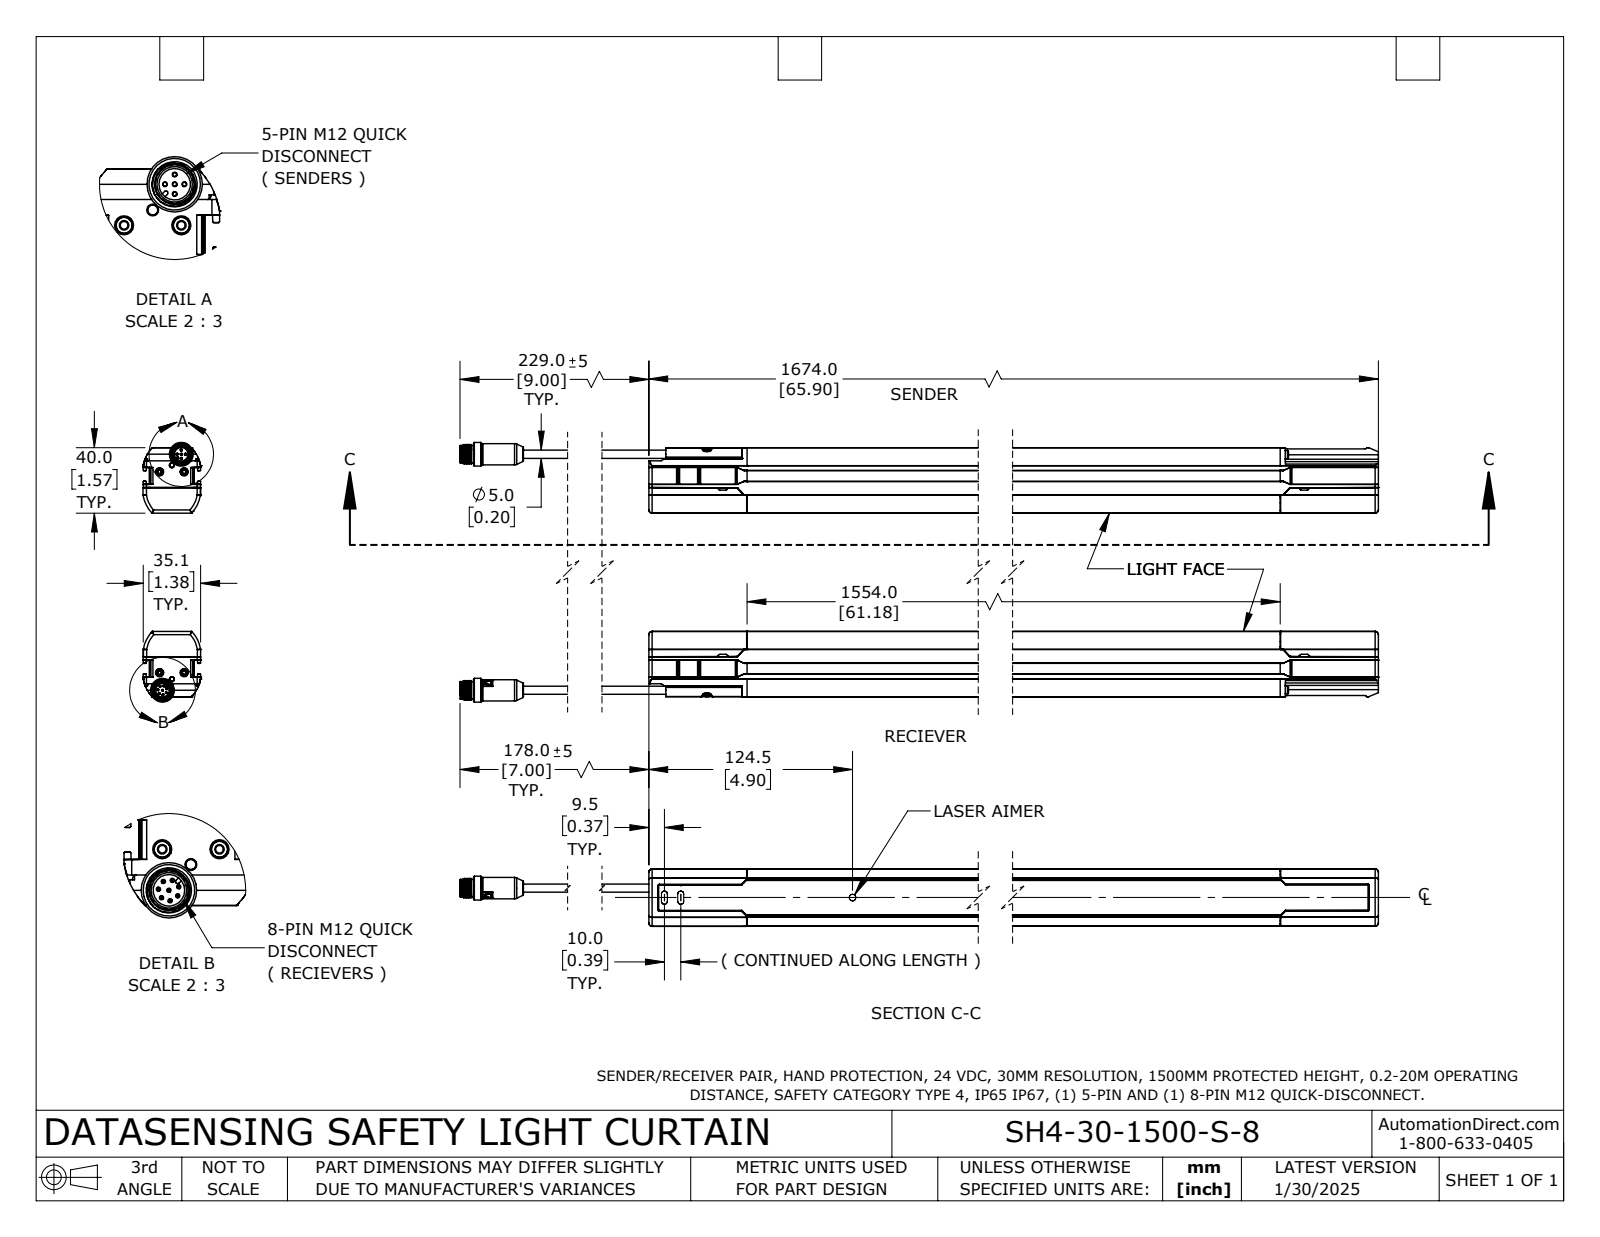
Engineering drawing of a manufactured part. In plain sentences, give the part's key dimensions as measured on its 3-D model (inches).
The part is named "SH4-30-1500-S-8". Its 3-D file was written by "SolidWorks 2024 (AUTOMOTIVE_DESIGN)". It is 4 solids with 2608 faces: 1186 planar, 784 cylindrical and 638 other. Overall it measures 68.398 by 6.248 by 1.384 inches. Its volume is 217.9 cubic inches and its surface area 918.1 square inches. Round holes: 4 of diameter 0.079, 4 of diameter 0.118, 4 of diameter 0.197, 2 of diameter 0.1, 2 of diameter 0.1, 2 of diameter 0.101, 2 of diameter 0.101, 2 of diameter 0.325, 2 of diameter 0.382, 2 of diameter 0.407, 2 of diameter 0.425, 1 of diameter 0.11. Round bosses or shafts: 10 of diameter 0.197, 8 of diameter 0.087, 8 of diameter 0.031, 5 of diameter 0.039, 4 of diameter 0.172, 2 of diameter 0.571, 2 of diameter 0.512, 2 of diameter 0.417. Partial cylindrical surfaces (rounded edges, fillets, slot ends): 164 of radius 0.01, 66 of radius 0.016, 50 of radius 0.02, 36 of radius 0.008, 20 of radius 0.031, 12 of radius 0.031, 12 of radius 0.079, 10 of radius 0.059. The main face-to-face distances are 1.496, 4.496, 0.156, 1.222, 3, 5.992, 1.378, 1.067, 4.634, 0.069. The hole center spacings are 0.866, 5.163, 5.235, 0.429, 0.591, 0.672, 4.831, 4.867.
